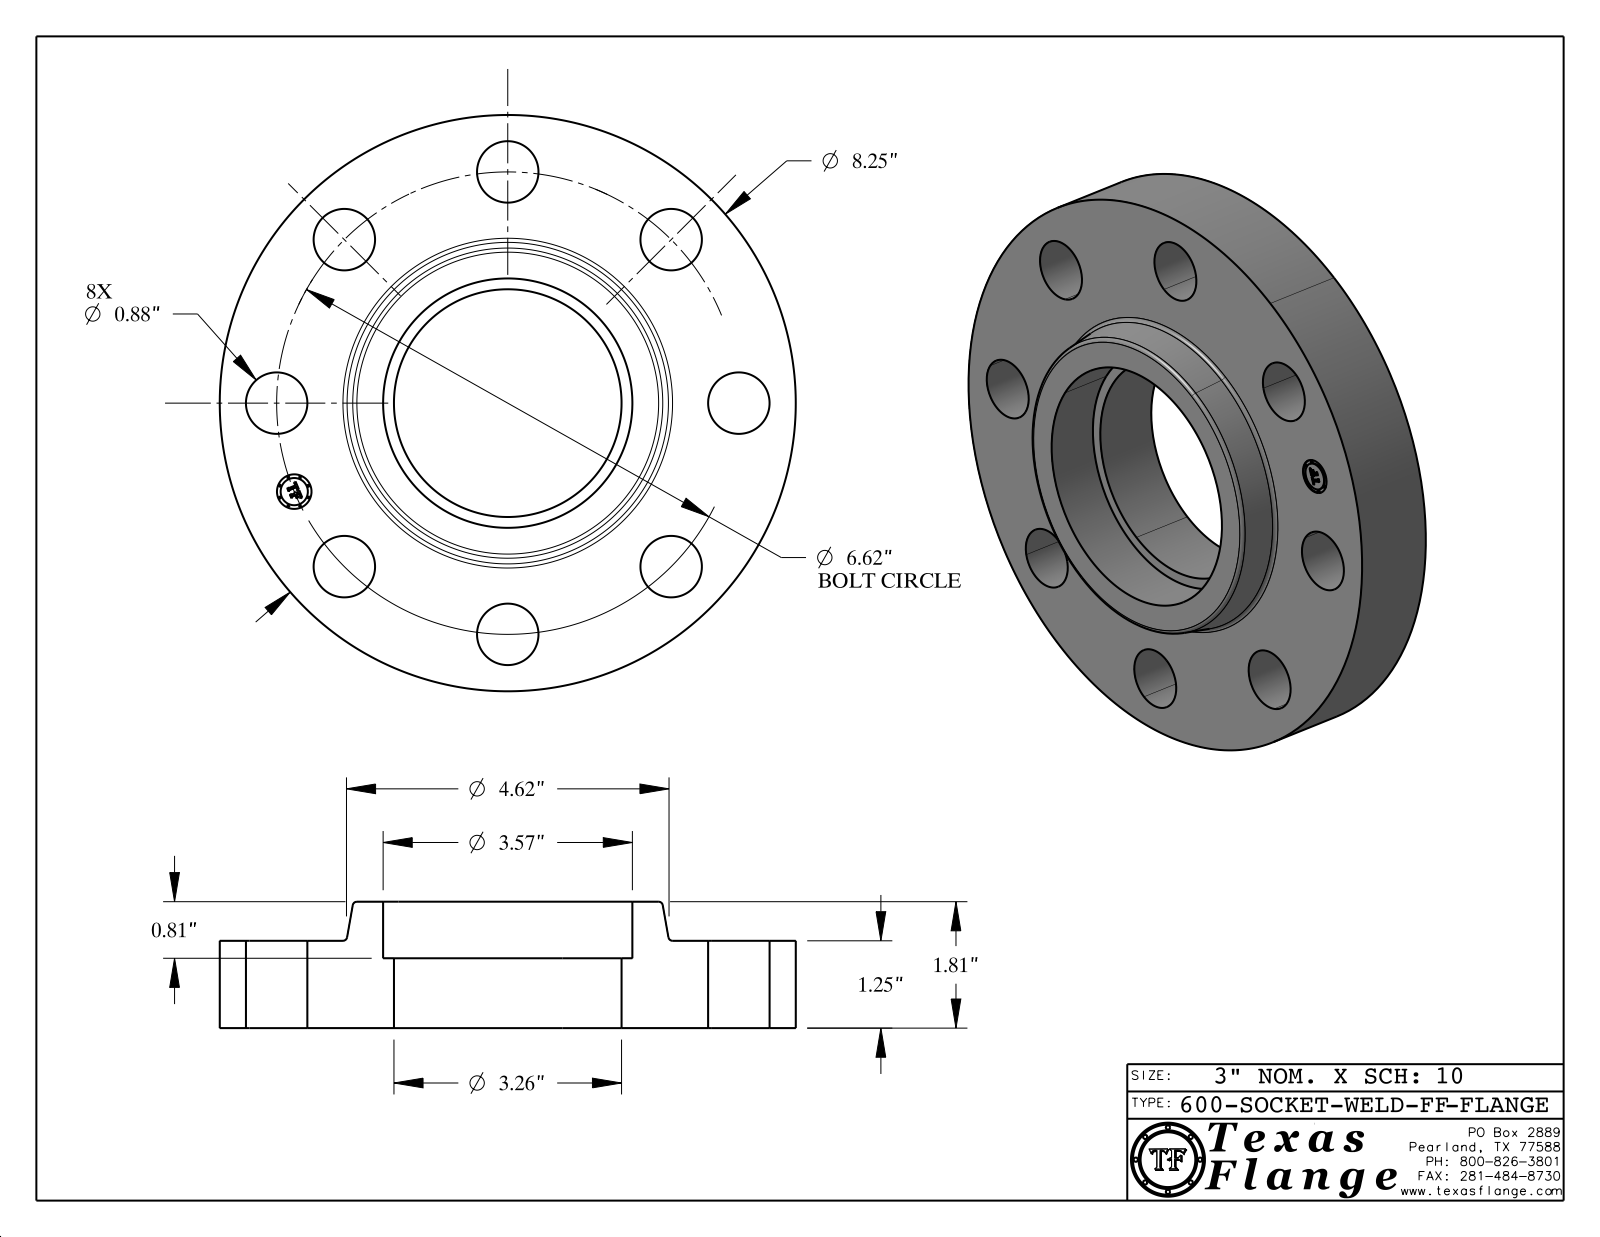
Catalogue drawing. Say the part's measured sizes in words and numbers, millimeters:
The part is named "600-SOCKET-WELD-FF". Its 3-D file was written by "CATIA V5 STEP AP214 (AUTOMOTIVE_DESIGN)". It is 1 solid with 417 faces: 369 planar, 42 cylindrical and 6 other. Overall it measures 209.6 by 209.6 by 46 millimeters. Its volume is 872 900 cubic millimeters and its surface area 107 200 square millimeters. Round holes: 8 of diameter 22.4, 1 of diameter 12.6, 1 of diameter 82.8, 1 of diameter 90.7. Round bosses or shafts: 8 of diameter 0.8, 1 of diameter 209.6, 1 of diameter 9.9. The main face-to-face distances are 31.8, 46, 14.2, 25.4, 6.4, 20.6, 0.4, 31.4, 6, 14.6. The hole center spacings are 84.1, 64.3, 155.3, 118.9, 118.9, 32.8, 93.4, 164.9.
